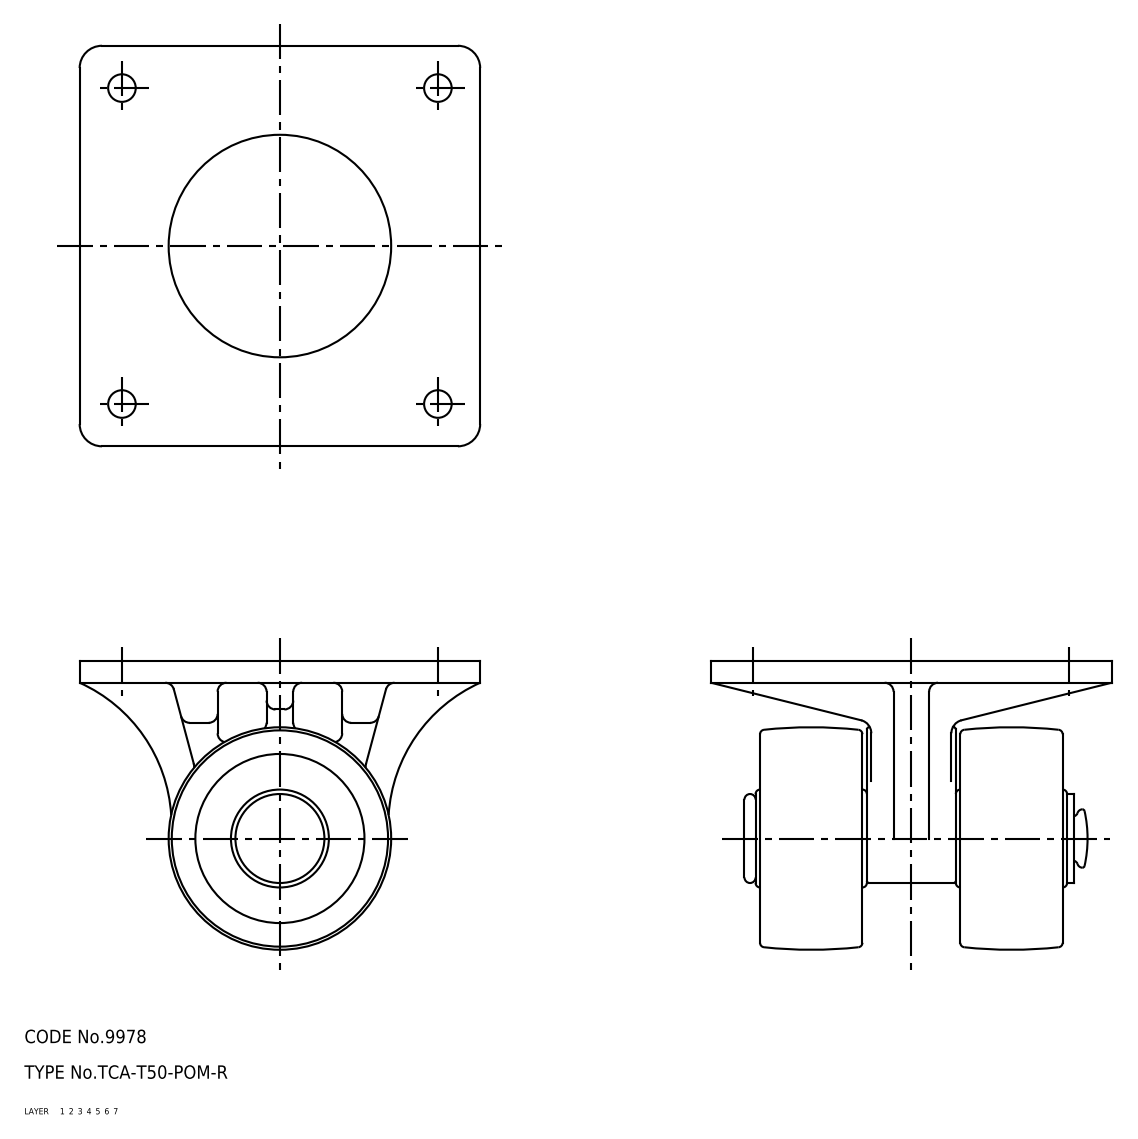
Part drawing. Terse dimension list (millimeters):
name: caster; TCA-T50-POM-R
written by: SolidWorks 2015 (AUTOMOTIVE_DESIGN)
unit: mm
bodies: 1 solid, 507 faces (91 planar, 206 cylindrical, 210 other)
size: 90.19 × 90 × 65
volume: 149 443 mm³; area: 52 308 mm²
holes: 4× ⌀6.2, 1× ⌀10.1, 1× ⌀10.2, 1× ⌀38, 1× ⌀50
bosses: 1× ⌀50, 1× ⌀22, 1× ⌀20, 1× ⌀10
rounds: 46× R2, 16× R0.5, 14× R1, 12× R3, 4× R5, 2× R35, 1× R21, 1× R24.5
face distances: 5, 45, 15.5, 7.5, 3.5, 7, 8, 1, 1.5, 29.5
hole spacings: 50.2, 71, 100.41
